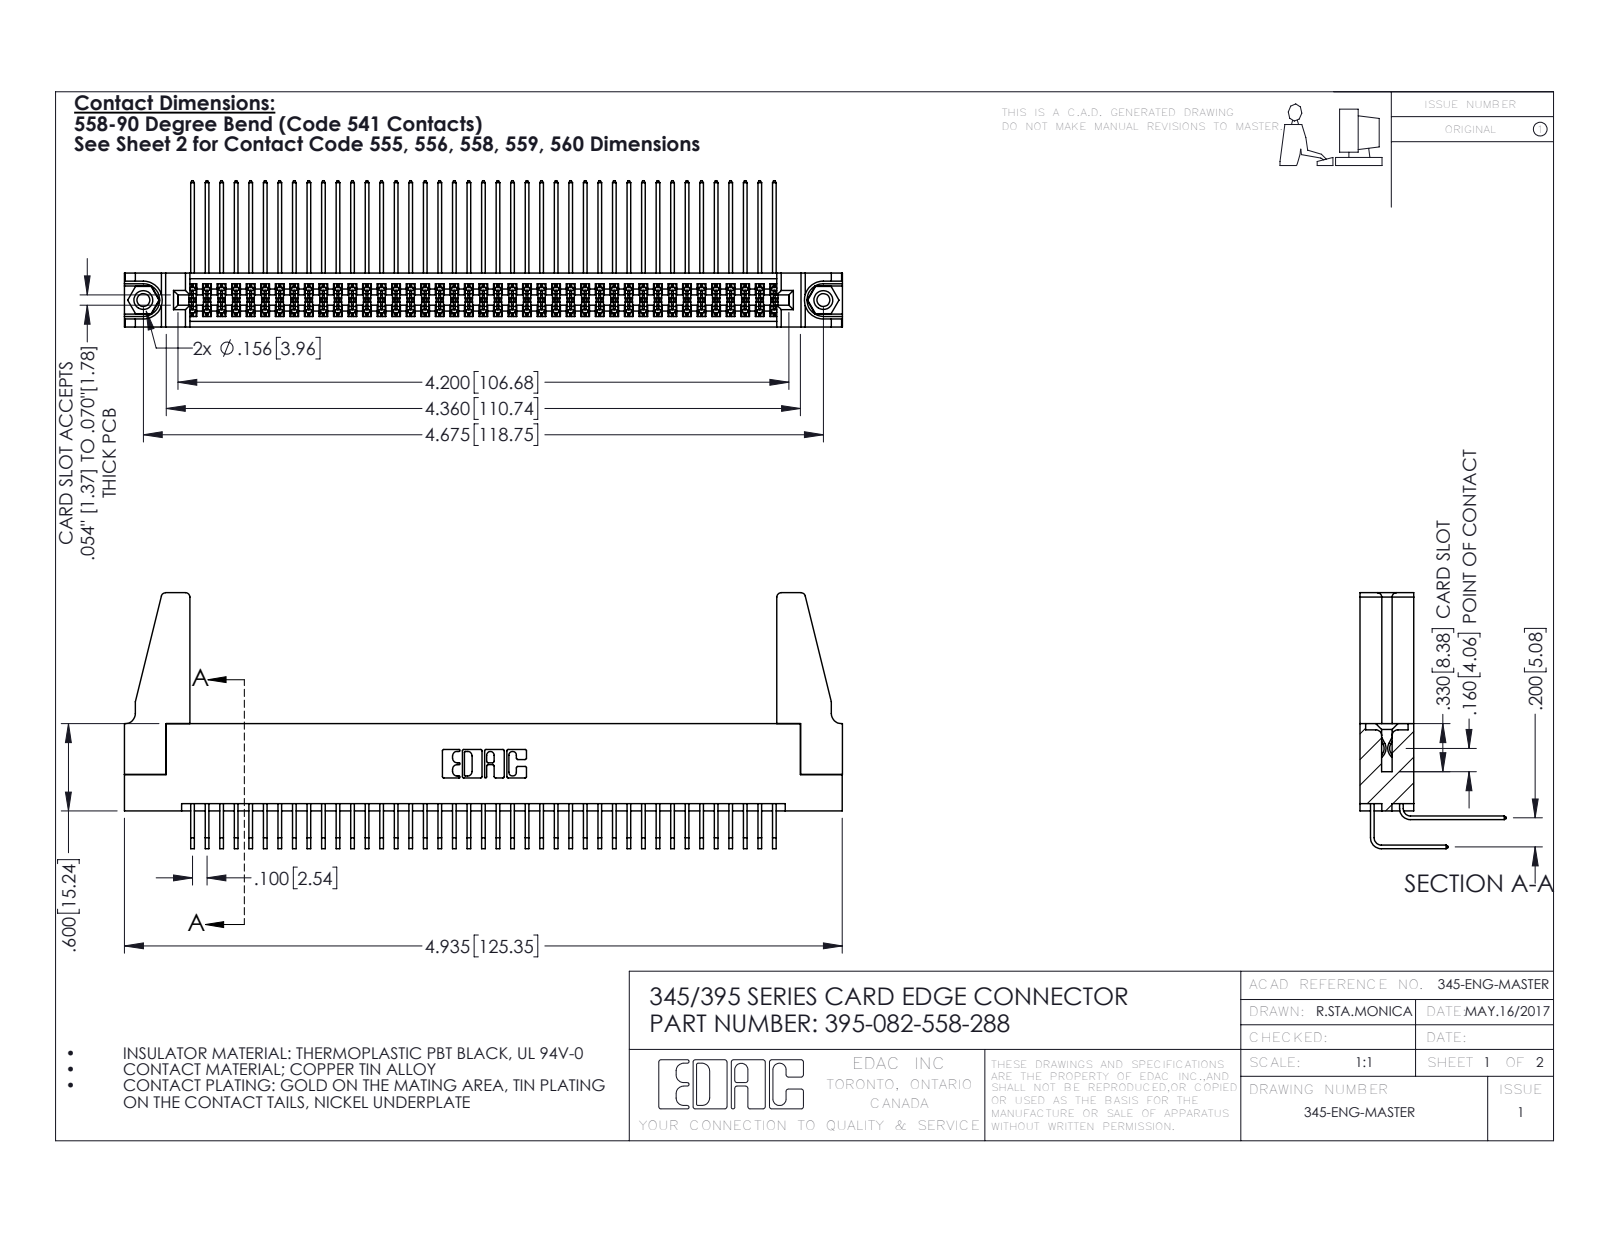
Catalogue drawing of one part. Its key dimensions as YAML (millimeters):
part_name: "395-082-558-288; 345-220-078_345-220-088; 345-250-001_345-250-001-102; 345-292-001_558 Tail - 2 (+2 more)"
step_written_by: "SolidWorks 2016 (CONFIG_CONTROL_DESIGN)"
units: millimeters
bodies: {solids: 87, faces: 4514, planar: 3022, cylindrical: 1476, other: 16}
overall_size: [125.4, 44.7, 25.5]
volume: 15900
surface_area: 24010
round_holes:
  - {diameter: 2.3, count: 2}
  - {diameter: 3.2, count: 2}
  - {diameter: 4, count: 2}
  - {diameter: 1.6, count: 1}
round_bosses_or_shafts:
  - {diameter: 3.9, count: 2}
partial_cylinders:
  - {radius: 0.2, count: 124}
  - {radius: 0.3, count: 22}
  - {radius: 0.8, count: 8}
  - {radius: 0.2, count: 6}
  - {radius: 0.8, count: 6}
  - {radius: 0.7, count: 3}
  - {radius: 0.4, count: 2}
  - {radius: 0.5, count: 2}
face_to_face_distances: [1.8, 7.6, 5.1, 9.4, 2.5, 6.9, 0.6, 5.7, 7.2, 0.6]
hole_center_spacings: [6.9, 112.8, 118.7]
